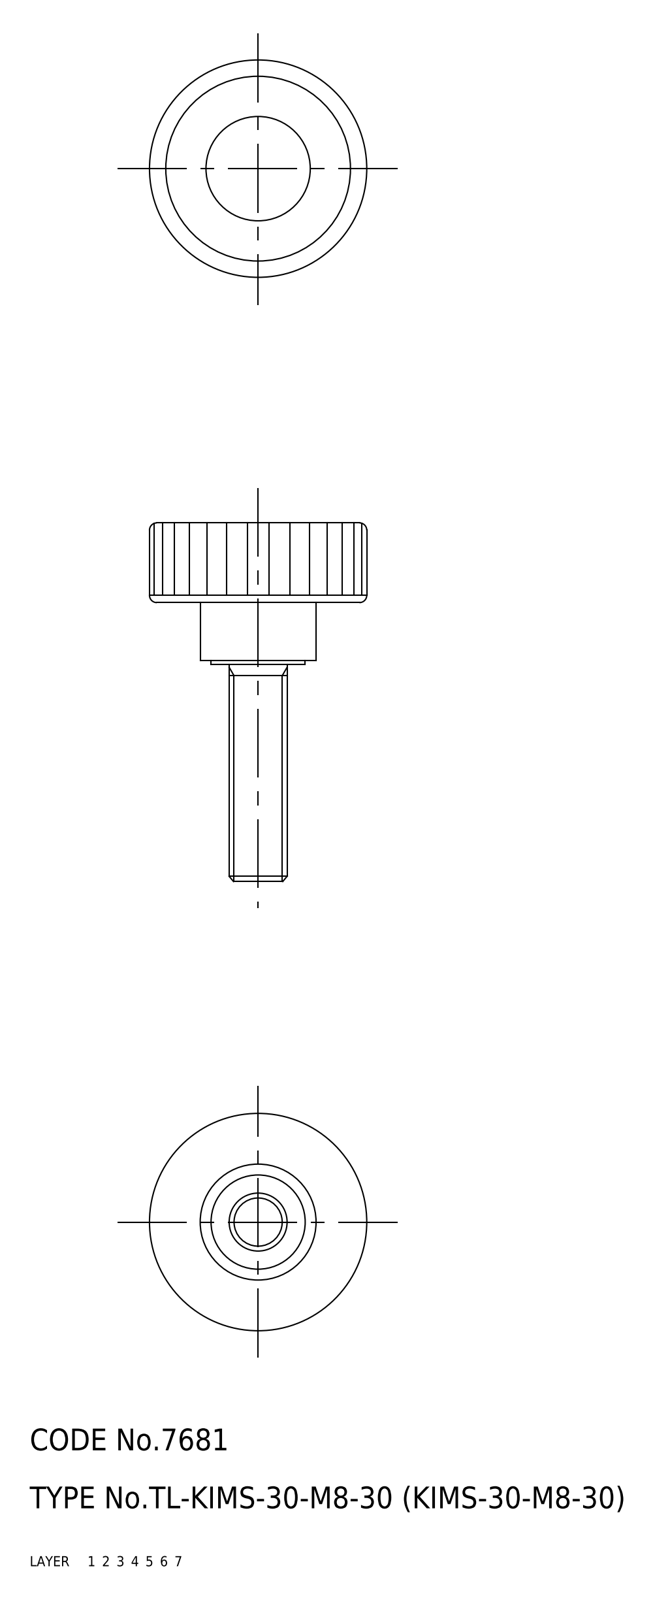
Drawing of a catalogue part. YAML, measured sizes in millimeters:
part_name: "screw; knob; KIMS_30_M8_30_4205_36"
step_written_by: "CADfix (AUTOMOTIVE_DESIGN)"
units: millimeters
bodies: {solids: 2, faces: 32, planar: 0, cylindrical: 0, other: 32}
overall_size: [49.5, 30, 30]
volume: 6473
surface_area: 5019
